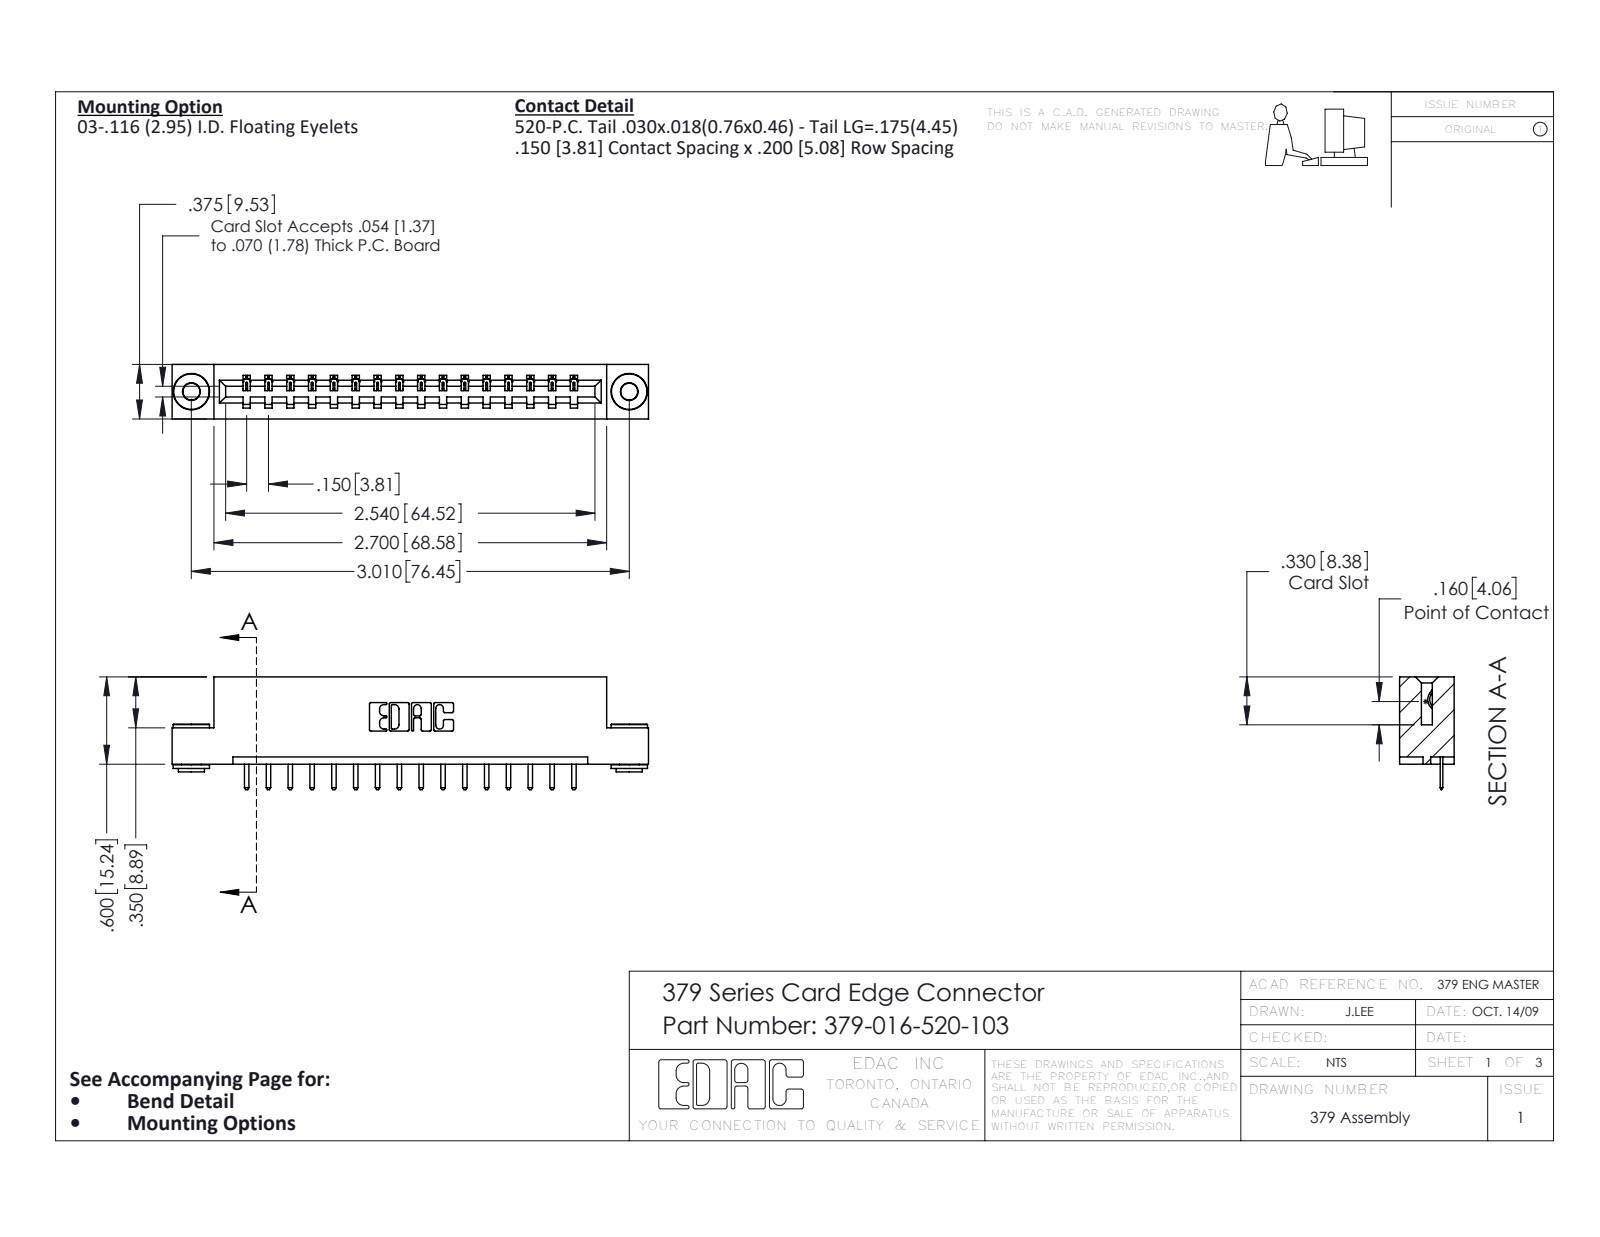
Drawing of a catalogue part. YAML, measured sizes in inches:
part_name: "345-250-002_345-250-002-102; 379-016-520-103; 379 Part_Flush - .156 Dia - TH; 345-292-001_345-293-120"
step_written_by: "SolidWorks 2020 (CONFIG_CONTROL_DESIGN)"
units: inches
bodies: {solids: 19, faces: 1144, planar: 784, cylindrical: 352, other: 8}
overall_size: [3.275, 0.775, 0.375]
volume: 0.513
surface_area: 13.23
round_holes:
  - {diameter: 0.116, count: 2}
  - {diameter: 0.156, count: 2}
round_bosses_or_shafts:
  - {diameter: 0.25, count: 2}
  - {diameter: 0.18, count: 2}
  - {diameter: 0.136, count: 2}
partial_cylinders:
  - {radius: 0.01, count: 34}
  - {radius: 0.006, count: 32}
  - {radius: 0.01, count: 22}
  - {radius: 0.007, count: 6}
  - {radius: 0.031, count: 6}
  - {radius: 0.026, count: 3}
  - {radius: 0.014, count: 1}
  - {radius: 0.022, count: 1}
face_to_face_distances: [0.3, 0.375, 0.075, 0.6, 0.15, 0.225, 0.45, 0.2, 0.75, 0.9]
hole_center_spacings: [3.01]
